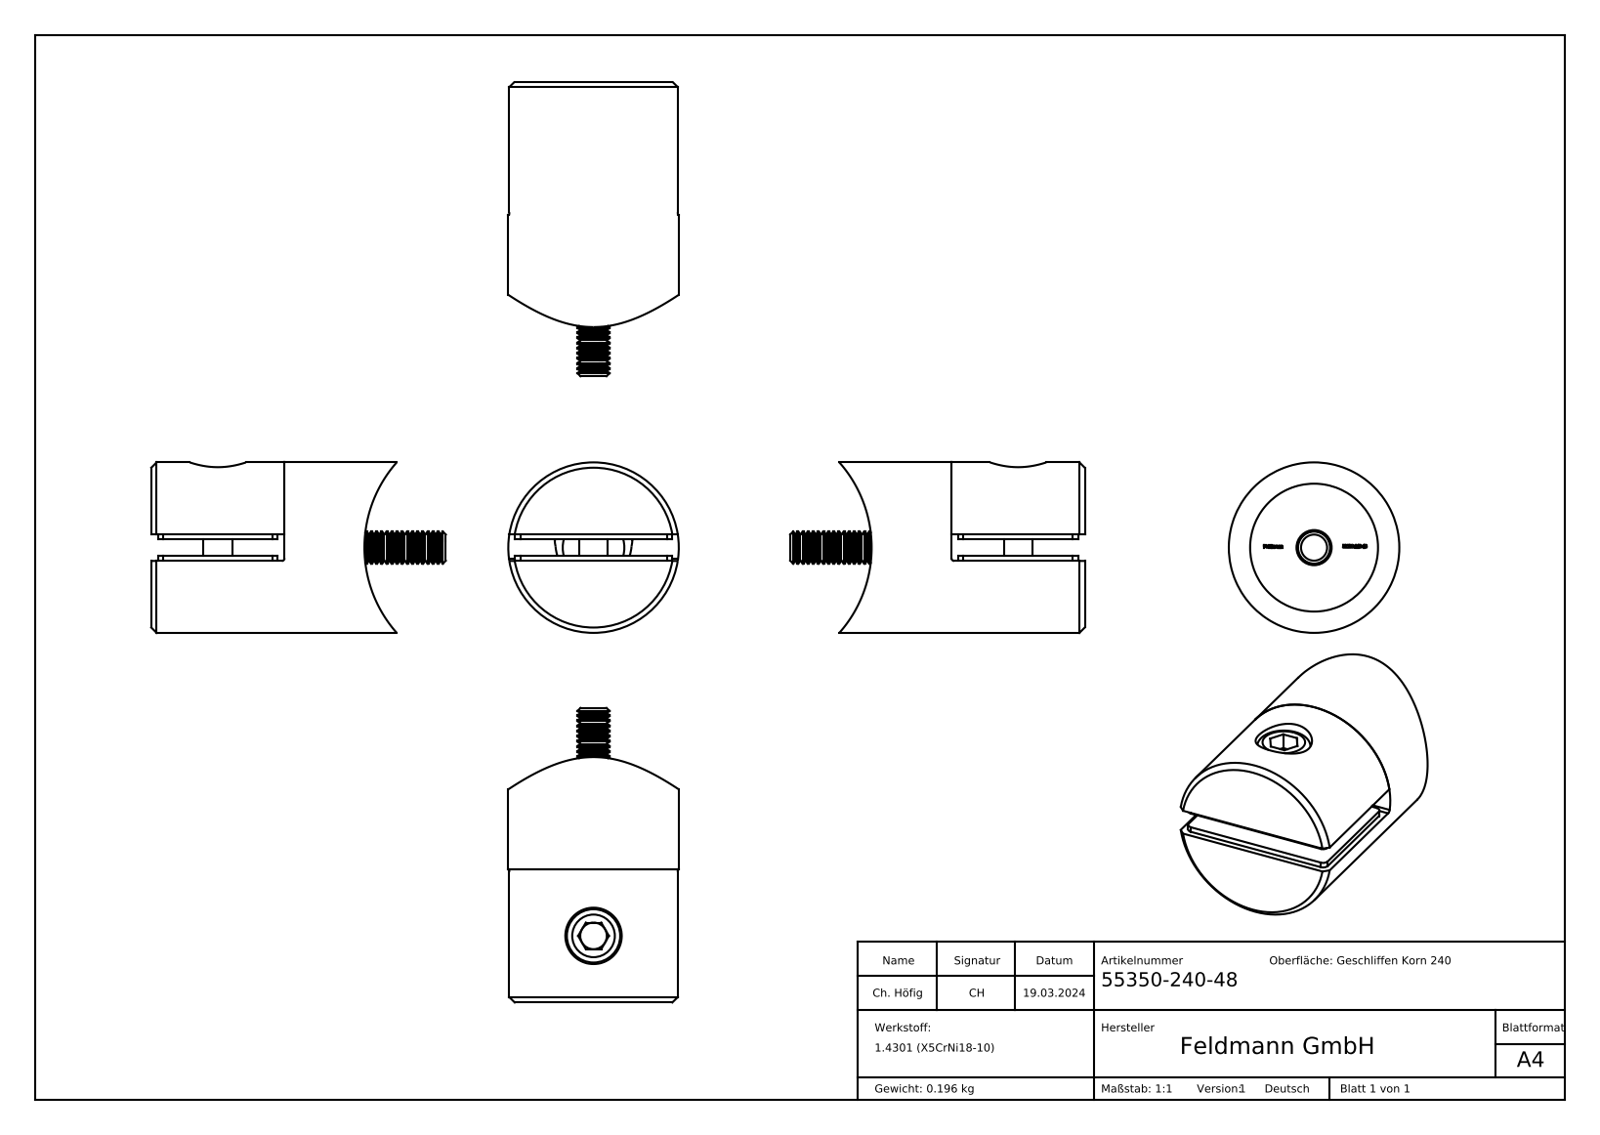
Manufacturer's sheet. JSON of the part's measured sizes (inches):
{"part_name": "55350-240-48; DIN 912 M6x18_DIN 912 M6x18; 5533X-240 Teil1_55350-240-48 Teil1; 5533X-240 Teil2_55350-240-XX Teil2 (+2 more)", "step_written_by": "SolidWorks 2018 (CONFIG_CONTROL_DESIGN)", "units": "inches", "bodies": {"solids": 6, "faces": 442, "planar": 203, "cylindrical": 55, "other": 184}, "overall_size": [2.176, 1.26, 1.26], "volume_in3": 1.627, "surface_area_in2": 21.41, "round_holes": [[0.157, 2], [0.197, 1], [0.256, 1], [0.26, 1], [0.276, 1], [0.417, 1], [0.945, 1]], "round_bosses_or_shafts": [[0.157, 2], [1.26, 1], [0.456, 1], [0.394, 1], [0.236, 1], [0.211, 1]], "partial_cylinders_radius": [[0.039, 4], [0.02, 1], [0.281, 1], [0.287, 1], [0.951, 1]], "face_to_face_distances": [0.157, 0.039, 0.197, 0.118, 0.984, 0.374, 1.358, 0.295, 0.413, 0.256], "hole_center_spacings": [0.376, 0.512]}
